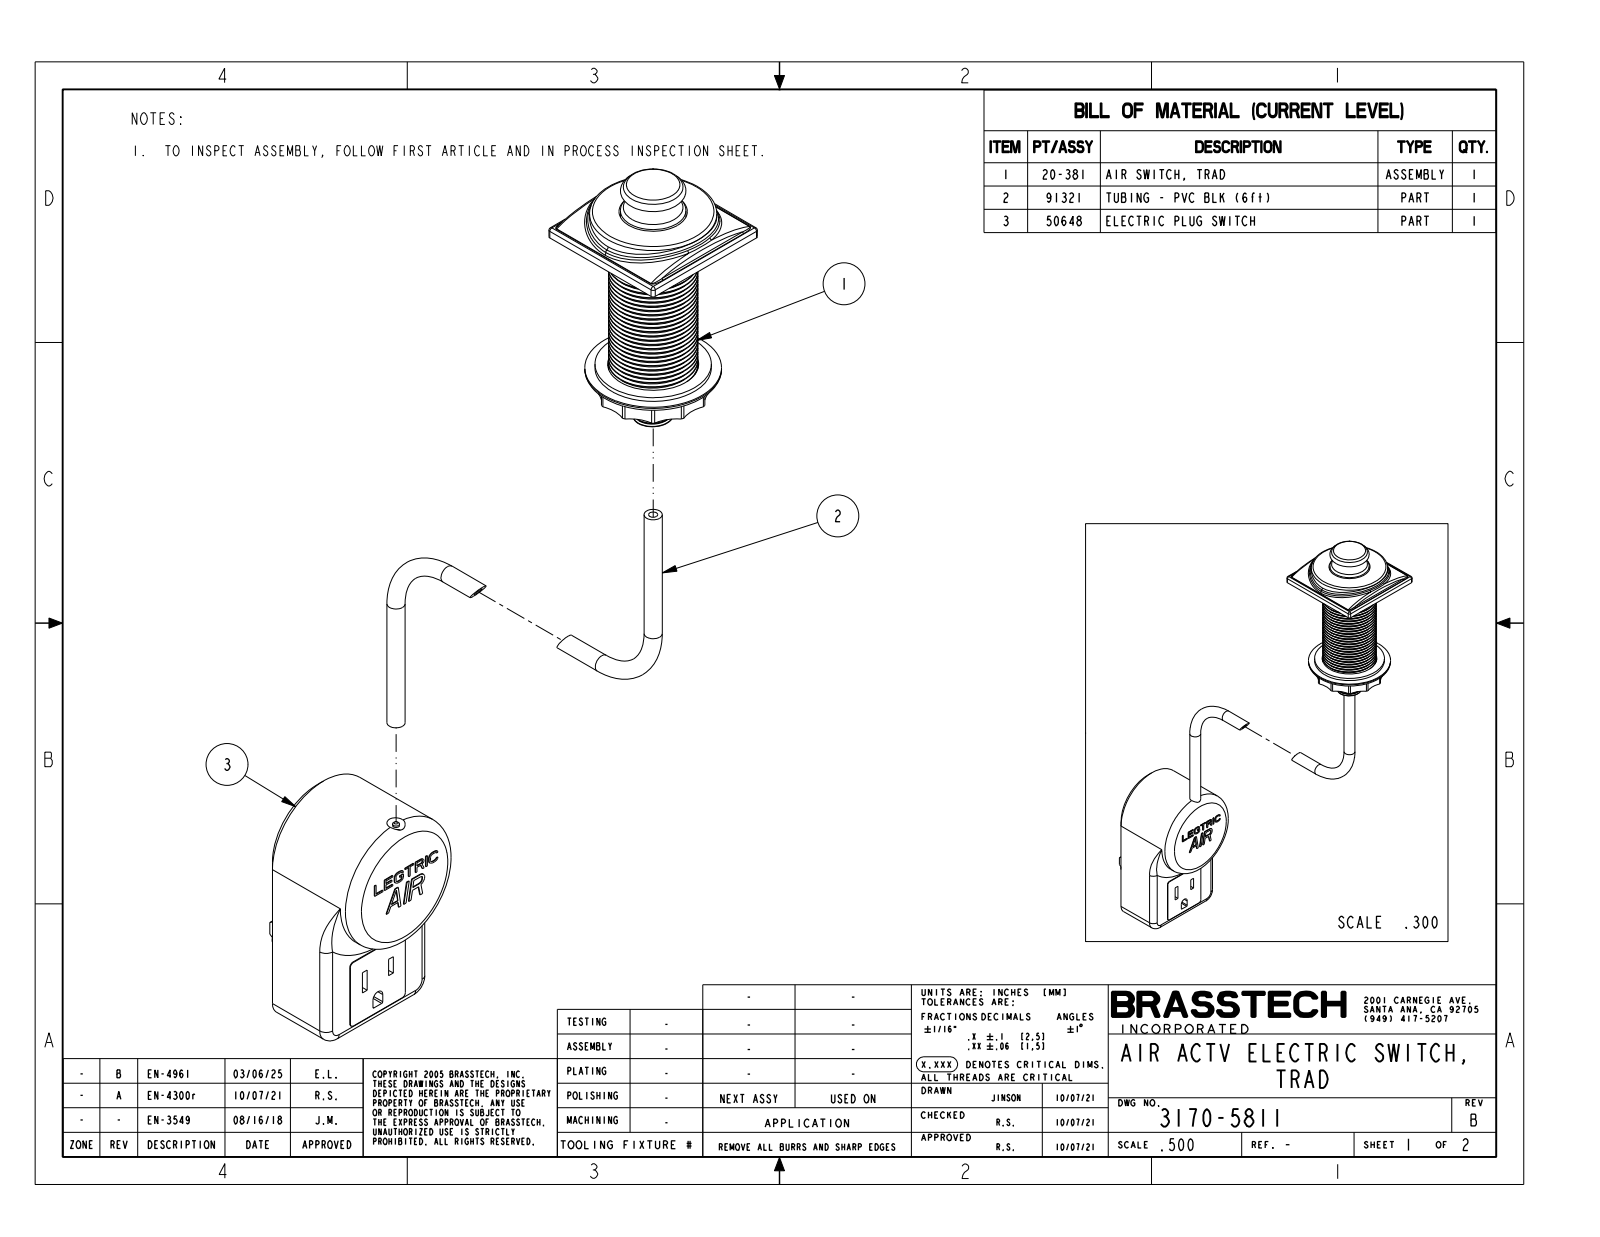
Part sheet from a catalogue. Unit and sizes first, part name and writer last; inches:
Units: inches
Overall size (bounding box): 12.984 × 8.398 × 2.05
Round holes (diameter × count): ⌀0.125 ×4, ⌀0.94 ×1, ⌀1.25 ×1
Round bosses / shafts (diameter × count): ⌀0.25 ×3, ⌀1.99 ×1, ⌀1.88 ×1, ⌀1.75 ×1, ⌀1.6 ×1, ⌀1.23 ×1, ⌀1.153 ×1, ⌀1.135 ×1
Partial cylindrical surfaces — rounded edges, fillets, slot ends (radius × count): R0.5 ×12, R0.04 ×8, R0.02 ×6, R0.06 ×4, R0.125 ×3, R0.25 ×2, R0.095 ×1, R0.81 ×1
Main face-to-face distances: 1.99, 1.7, 0.08, 0.425, 0.36, 12.059, 12.484, 0.52, 1.18, 0.44
Hole centre spacings: 5
Volume: 14.5 in³ · Surface area: 72.22 in²
Bodies: 3 solids, 513 faces (260 planar, 161 cylindrical, 92 other)
Part name (STEP PRODUCT): 3170-5811
STEP written by: CREO PARAMETRIC BY PTC INC, 2018400 (AUTOMOTIVE_DESIGN)
